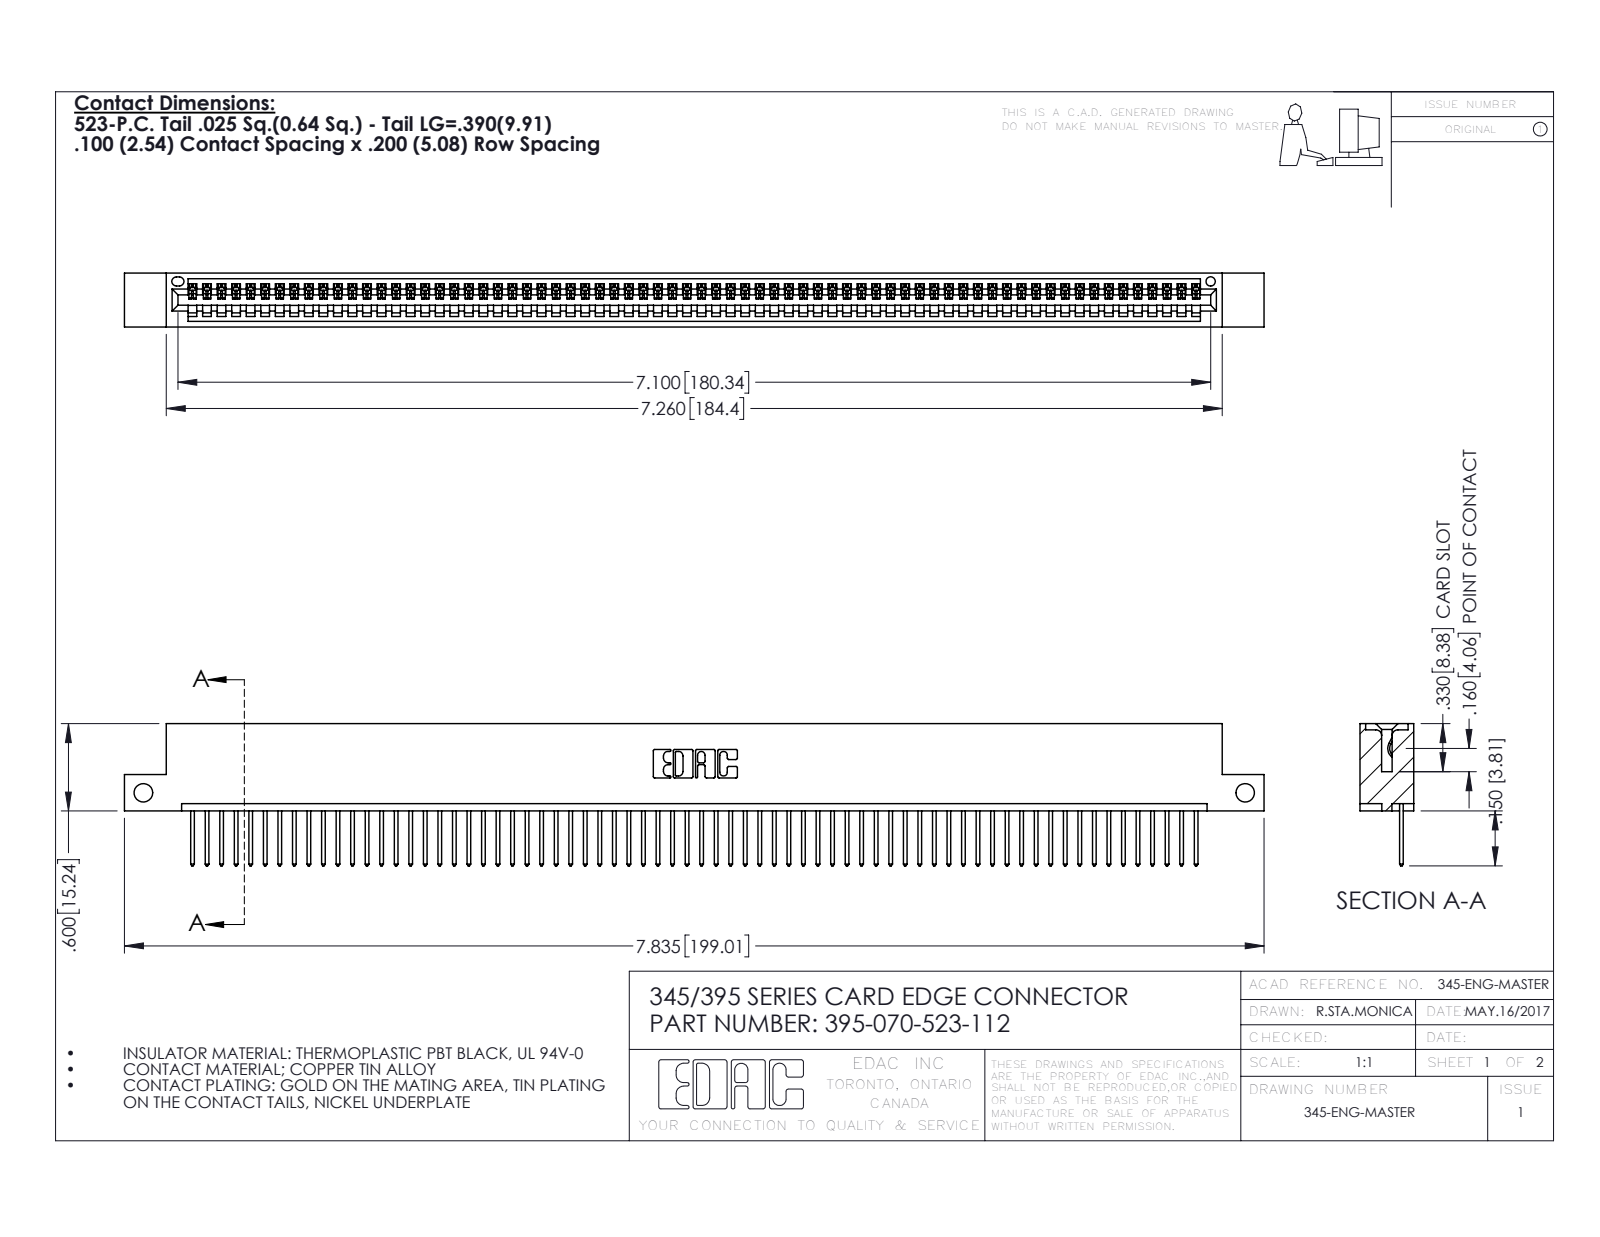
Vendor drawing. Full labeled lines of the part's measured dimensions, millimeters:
Part name (STEP PRODUCT): 345-292-001_345-293-123; 395-070-523-112; 345 Part_Flush Mounting Lugs - Side Mount
STEP written by: SolidWorks 2016 (CONFIG_CONTROL_DESIGN)
Units: millimetres
Bodies: 71 solids, 4186 faces (2880 planar, 1306 cylindrical, 0 other)
Overall size (bounding box): 199 × 24.8 × 9.4
Volume: 19 010 mm³ · Surface area: 25 590 mm²
Round holes (diameter × count): ⌀3.3 ×2, ⌀1.6 ×1
Partial cylindrical surfaces — rounded edges, fillets, slot ends (radius × count): R0.2 ×140, R0.3 ×140, R0.3 ×22, R0.2 ×6, R0.8 ×6, R0.7 ×3, R0.8 ×2, R1 ×2
Main face-to-face distances: 7.6, 1.8, 9.4, 5.1, 2.5, 6.9, 0.6, 5.7, 3.8, 1.8
Hole centre spacings: 192.4
